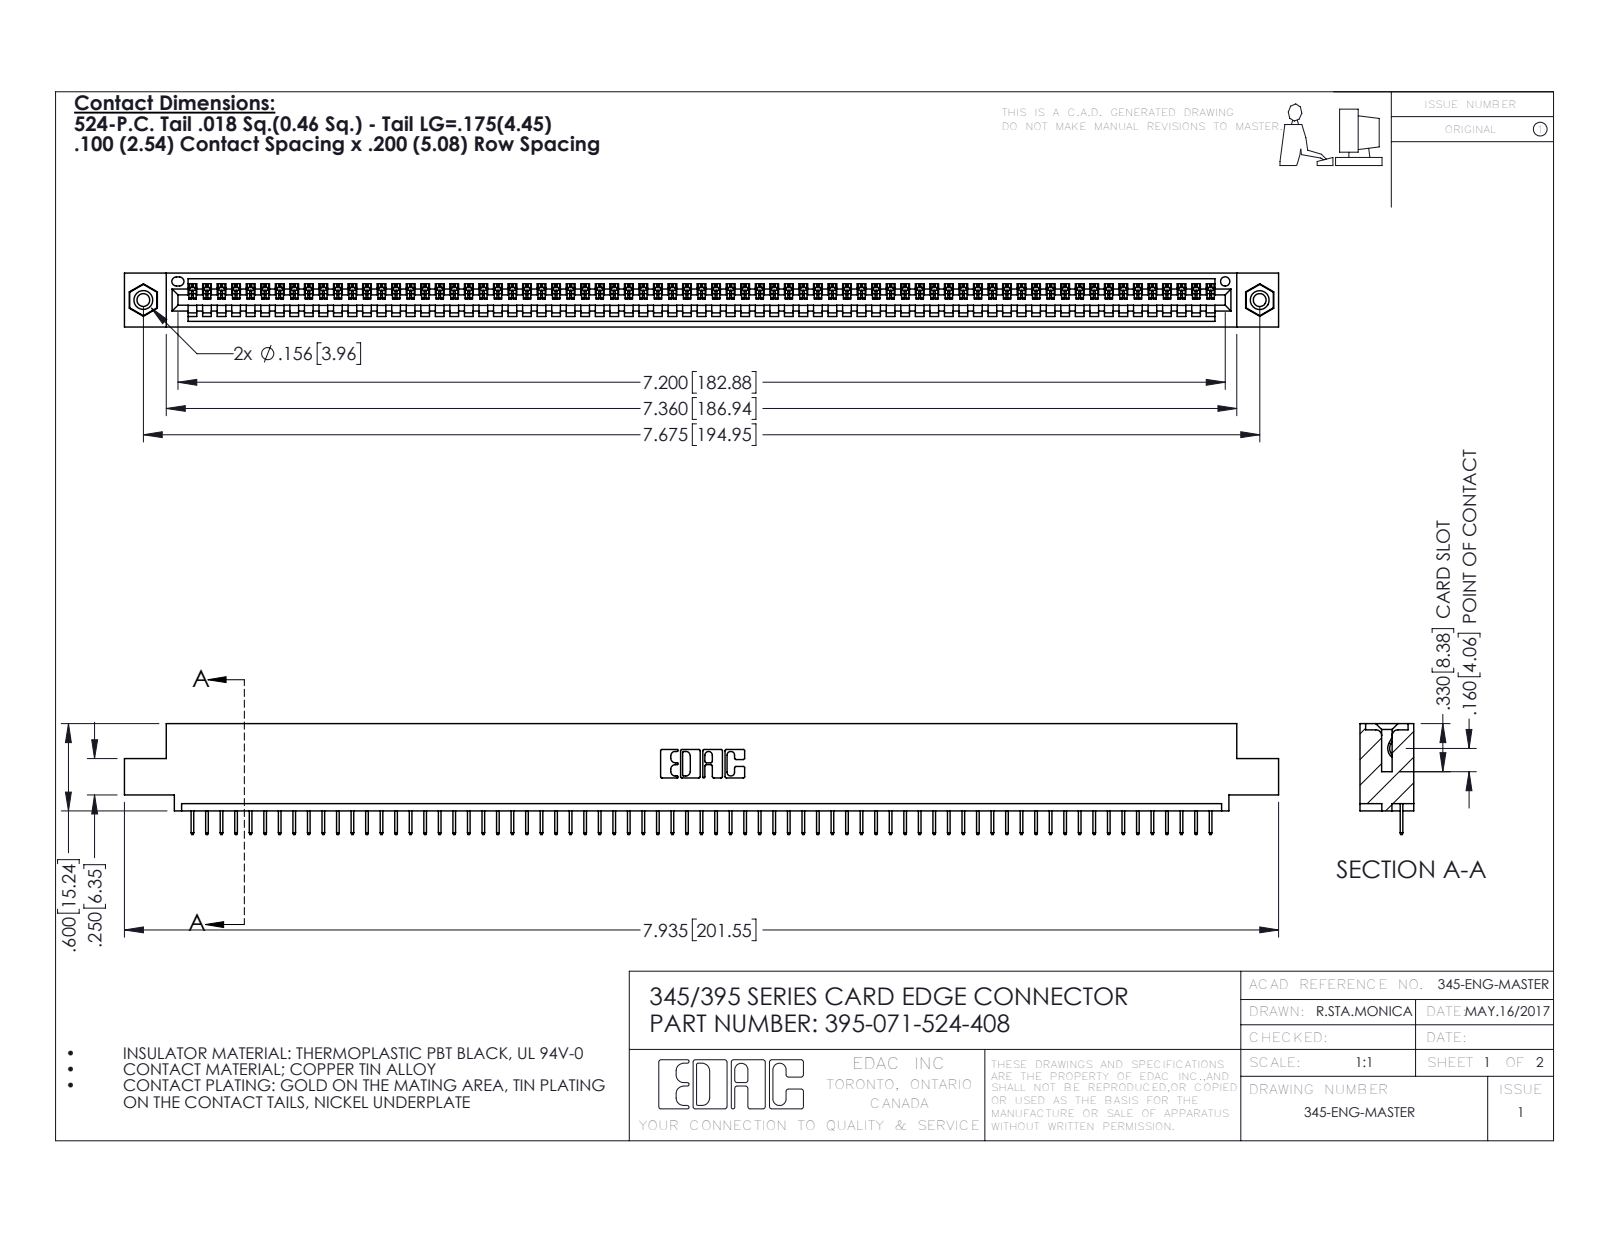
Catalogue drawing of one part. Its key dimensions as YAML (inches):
part_name: "345-250-001_345-250-003-102; 345-292-001_345-293-124; 395-071-524-408; 345 Part_0.110 Offset - 0.156 Dia-TI"
step_written_by: "SolidWorks 2016 (CONFIG_CONTROL_DESIGN)"
units: inches
bodies: {solids: 74, faces: 4592, planar: 3382, cylindrical: 1194, other: 16}
overall_size: [7.935, 0.762, 0.37]
volume: 1.161
surface_area: 38.56
round_holes:
  - {diameter: 0.089, count: 2}
  - {diameter: 0.125, count: 2}
  - {diameter: 0.156, count: 2}
  - {diameter: 0.064, count: 1}
round_bosses_or_shafts:
  - {diameter: 0.155, count: 2}
partial_cylinders:
  - {radius: 0.006, count: 142}
  - {radius: 0.01, count: 22}
  - {radius: 0.007, count: 6}
  - {radius: 0.031, count: 6}
  - {radius: 0.026, count: 3}
  - {radius: 0.031, count: 2}
  - {radius: 0.04, count: 2}
  - {radius: 0.014, count: 1}
face_to_face_distances: [0.072, 0.298, 0.37, 0.2, 0.098, 0.272, 0.025, 0.225, 0.072, 0.149]
hole_center_spacings: [0.27, 7.439, 7.675]
